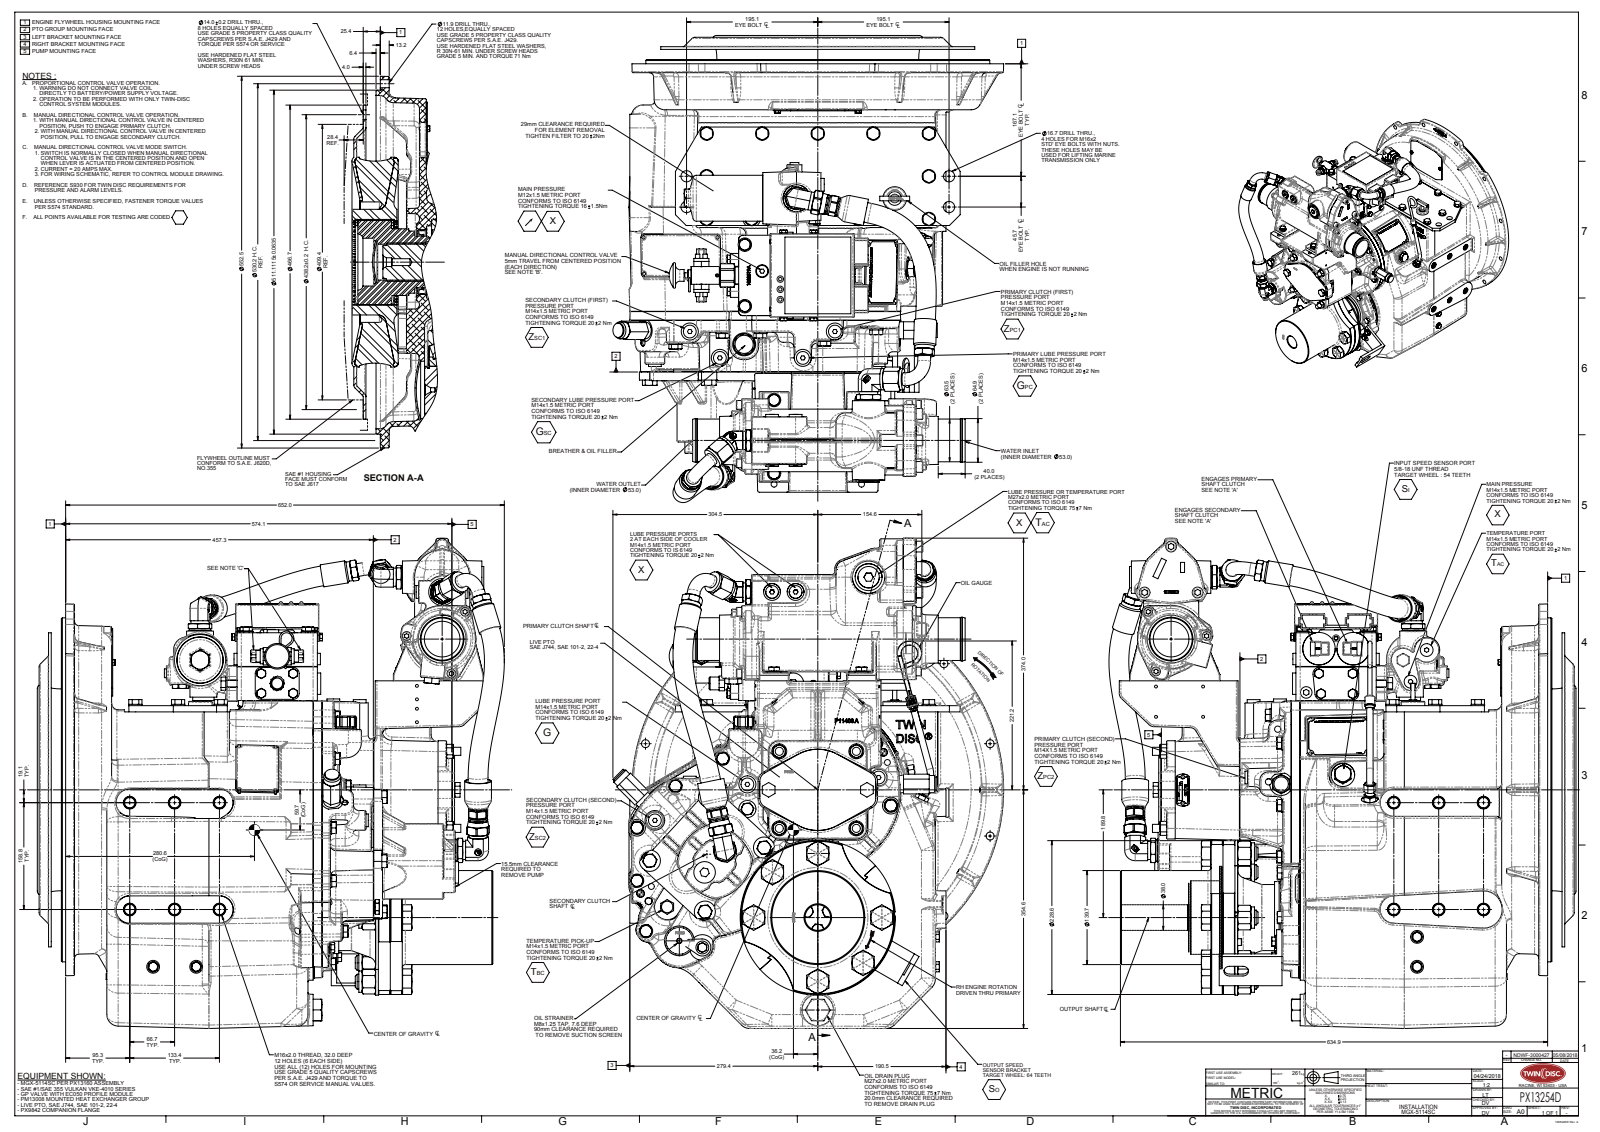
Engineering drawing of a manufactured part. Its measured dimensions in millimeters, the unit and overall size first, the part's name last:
Units: millimetres
Overall size (bounding box): 728.57 × 694.1 × 580.73
Round holes (diameter × count): ⌀11.91 ×12, ⌀4.2 ×8, ⌀14 ×8, ⌀18.82 ×8, ⌀8.8 ×6, ⌀16.67 ×4, ⌀25 ×4, ⌀9.3 ×3, ⌀10 ×3, ⌀3 ×2, ⌀4.8 ×2, ⌀10.72 ×2
Round bosses / shafts (diameter × count): ⌀20 ×23, ⌀19 ×11, ⌀19.05 ×8, ⌀13 ×7, ⌀31.8 ×6, ⌀31.64 ×5, ⌀19.85 ×5, ⌀16 ×5
Partial cylindrical surfaces — rounded edges, fillets, slot ends (radius × count): R2 ×71, R1 ×70, R1.52 ×60, R4 ×47, R8.13 ×44, R30.96 ×39, R2.03 ×34, R5.08 ×33
Main face-to-face distances: 0.42, 13.12, 323.16, 322.74, 13.54, 309.62, 9.27, 12.7, 310.04, 7.62
Hole centre spacings: 459.18, 137.23, 265.1, 265.11, 374.92, 512.14, 158.75, 219.1
Bodies: 0 solids, 5109 faces (1773 planar, 1360 cylindrical, 1976 other)
Part name (STEP PRODUCT): PX13254D
STEP written by: SolidWorks 2015 (AUTOMOTIVE_DESIGN)
